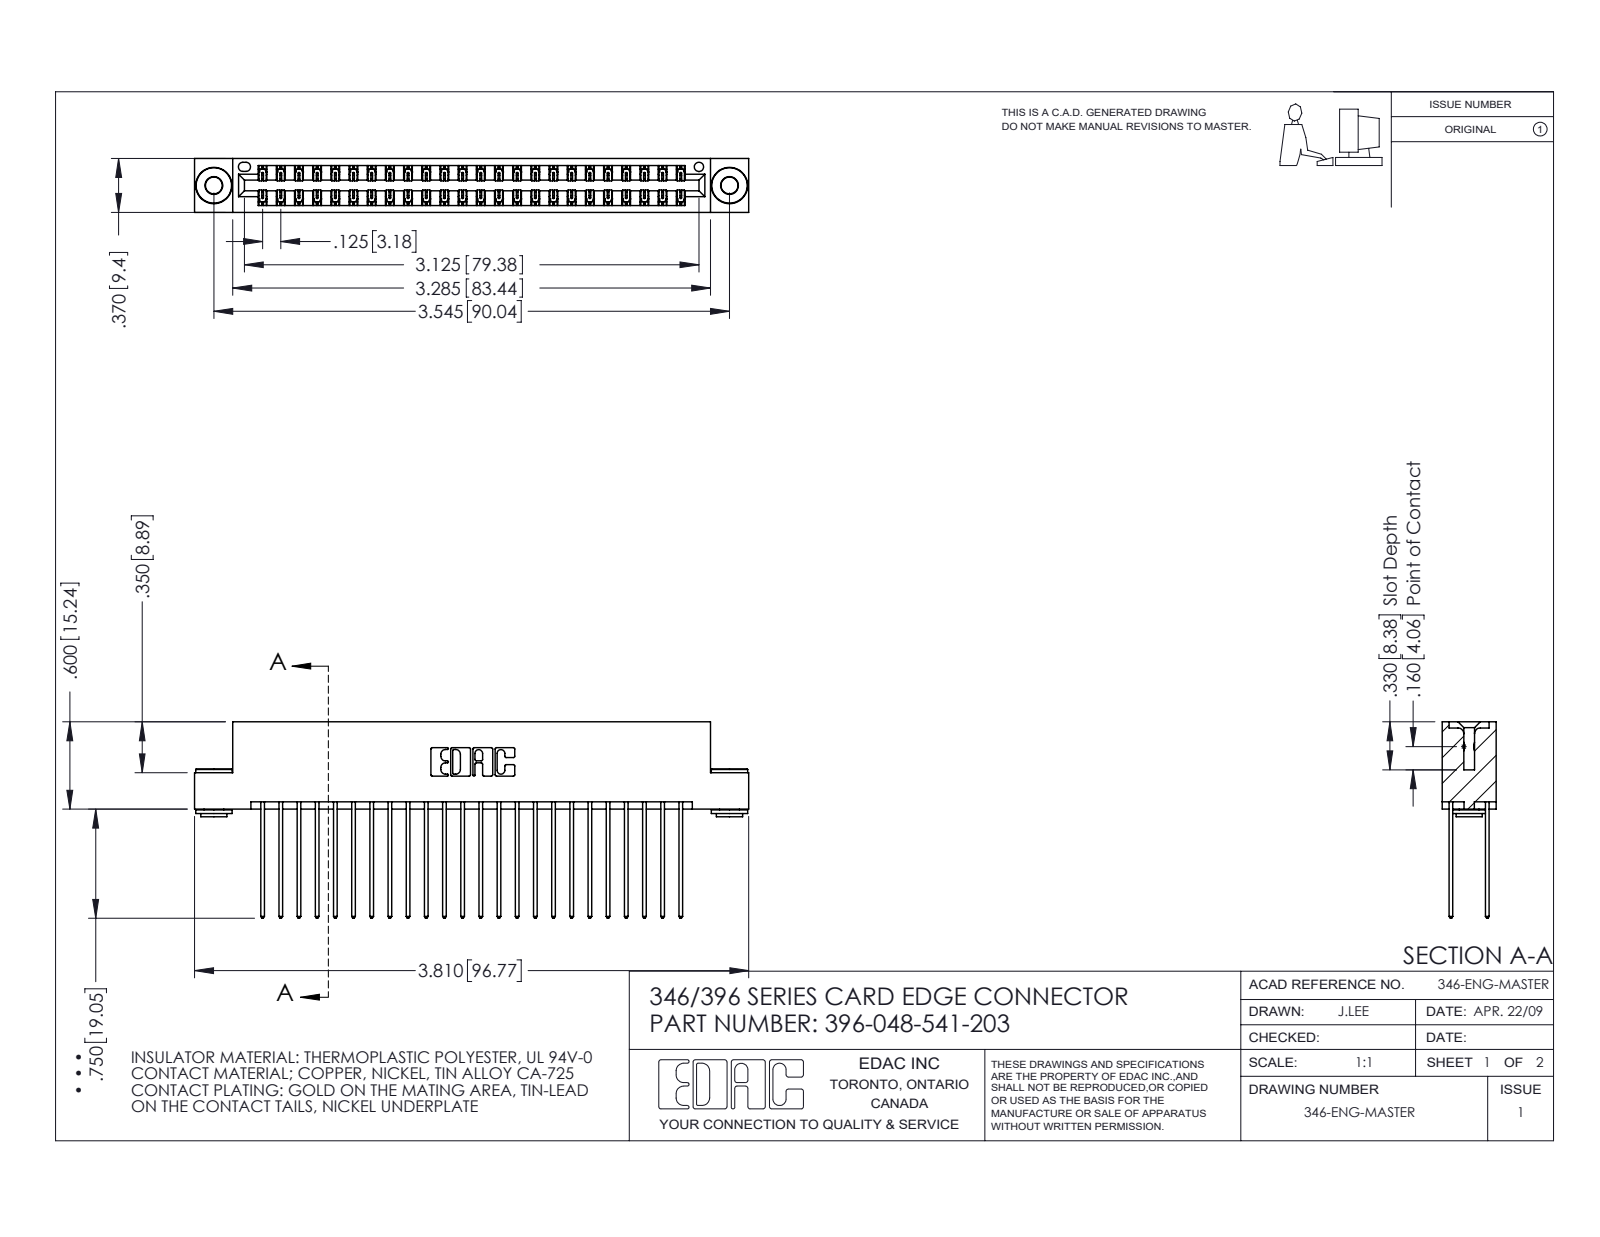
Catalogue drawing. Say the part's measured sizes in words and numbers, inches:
The part is named "345-250-002_345-250-002-102; 346 Part_Flush Mounting Lugs - 0.156 Dia-TH; 345-292-001_345-293-141; 396-048-541-203". Its 3-D file was written by "SolidWorks 2016 (CONFIG_CONTROL_DESIGN)". It is 51 solids with 2656 faces: 1766 planar, 882 cylindrical and 8 other. Overall it measures 3.81 by 1.35 by 0.37 inches. Its volume is 0.585 cubic inches and its surface area 22.38 square inches. Round holes: 2 of diameter 0.116, 2 of diameter 0.156, 1 of diameter 0.064. Round bosses or shafts: 2 of diameter 0.25, 2 of diameter 0.18, 2 of diameter 0.136. Partial cylindrical surfaces (rounded edges, fillets, slot ends): 72 of radius 0.006, 48 of radius 0.01, 22 of radius 0.01, 6 of radius 0.007, 6 of radius 0.031, 3 of radius 0.026, 2 of radius 0.014, 2 of radius 0.022. The main face-to-face distances are 0.048, 0.322, 0.25, 0.025, 0.072, 0.298, 0.37, 0.275, 0.225, 0.148. The hole center spacings are 0.246, 3.337, 3.545.
